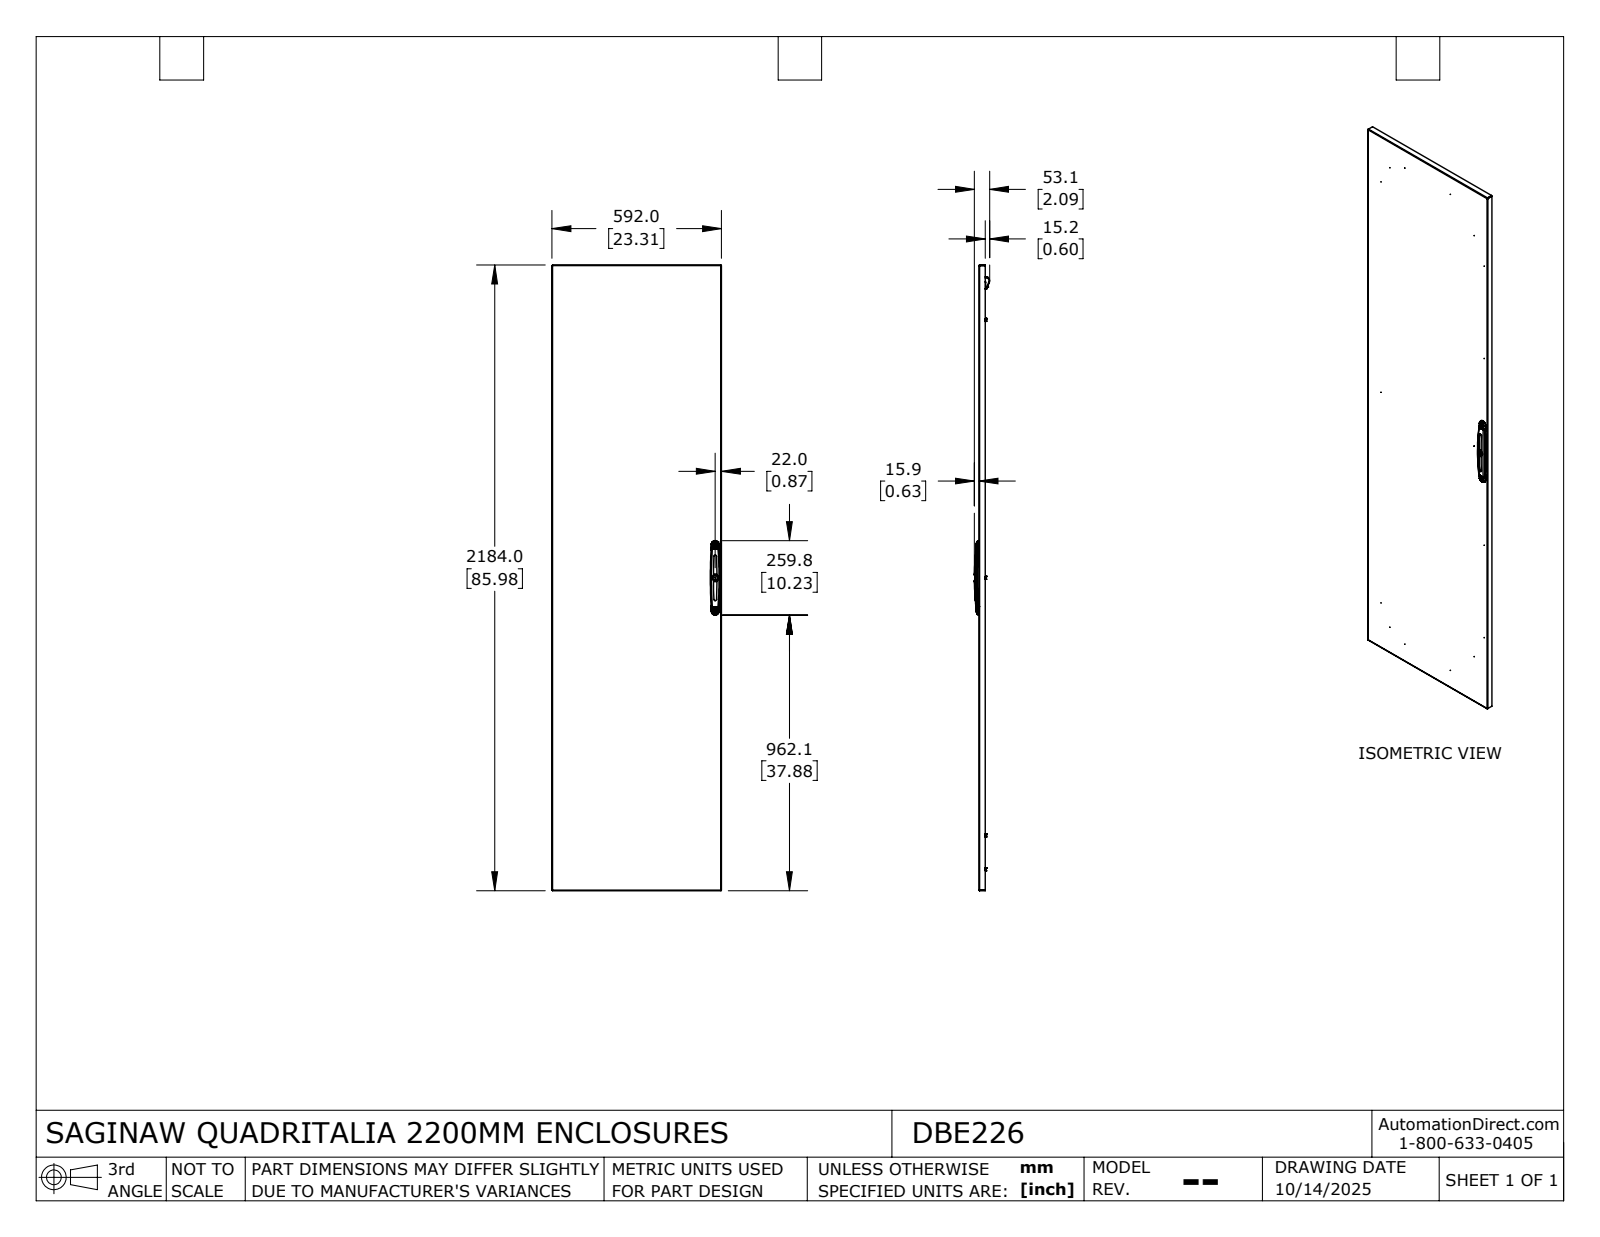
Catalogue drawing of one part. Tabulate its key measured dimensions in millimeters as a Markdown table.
| quantity | value |
| --- | --- |
| part name | DBE226 |
| STEP written by | SolidWorks 2024 (AUTOMOTIVE_DESIGN) |
| units | millimeters |
| bodies | 1 solid, 1529 faces (556 planar, 457 cylindrical, 516 other) |
| overall size | 2184 × 592 × 53.11 |
| volume | 3 841 000 mm³ |
| surface area | 3 448 000 mm² |
| round holes (diameter × count) | 4.25 × 175, 9 × 22, 1 × 18, 4.92 × 6, 4.92 × 4, 3.4 × 2, 4.3 × 2, 4.5 × 2, 5.2 × 2, 6 × 2, 15 × 1 |
| round bosses / shafts (diameter × count) | 7 × 12, 6 × 12, 7.2 × 10, 10 × 1, 5 × 1 |
| partial cylindrical surfaces (radius × count) | 1 × 26, 4.5 × 16, 5.77 × 10, 0.5 × 9, 2 × 7, 2 × 4, 2.5 × 4, 4.59 × 4 |
| main face-to-face distances | 2, 1.5, 18.5, 20, 17, 460, 22, 590, 3.5, 20.5 |
| hole center spacings | 25, 50, 75, 104, 166.17, 362.09, 900, 1010.74 |
